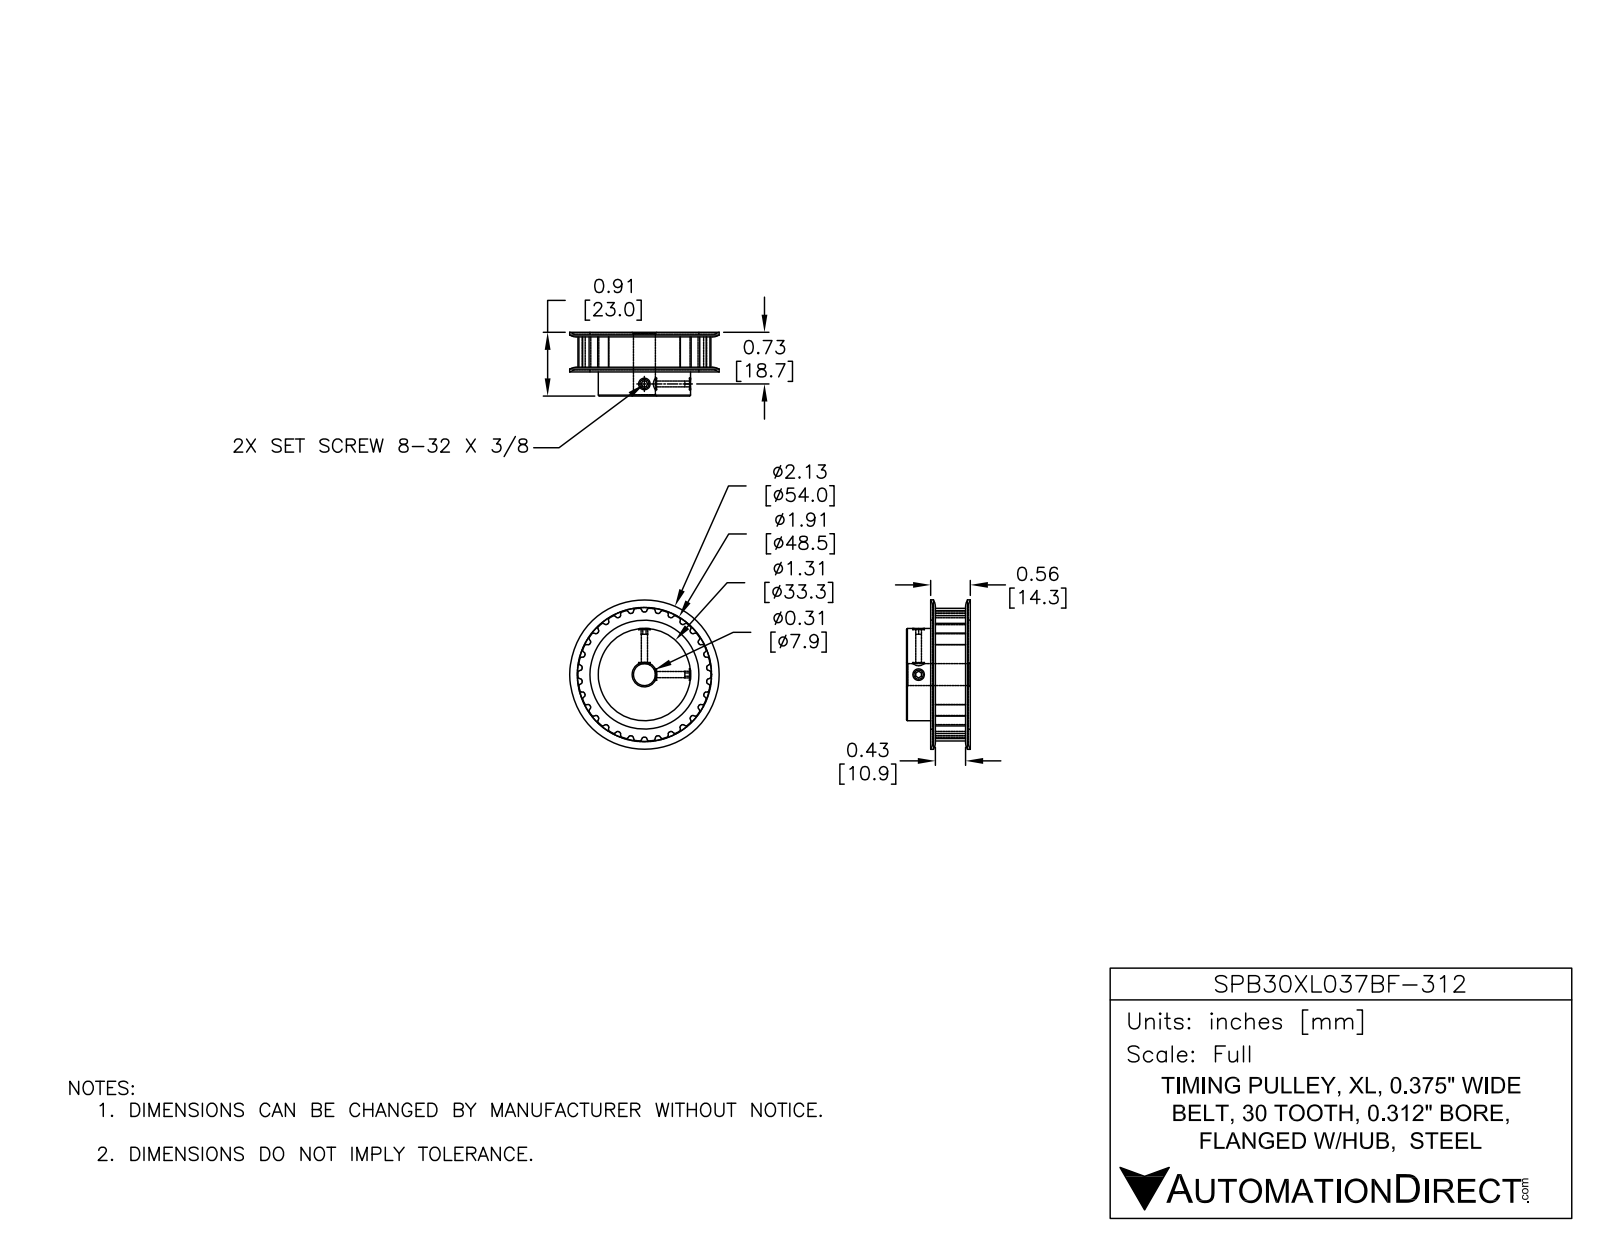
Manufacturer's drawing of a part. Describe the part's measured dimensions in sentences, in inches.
The part is named "SPB30XL037BF-312". Its 3-D file was written by "SolidWorks 2017 (AUTOMOTIVE_DESIGN)". It is 3 solids with 323 faces: 114 planar, 189 cylindrical and 20 other. Overall it measures 2.126 by 2.126 by 0.907 inches. Its volume is 1.897 cubic inches and its surface area 15.62 square inches. Round holes: 2 of diameter 0.136, 1 of diameter 0.313. Round bosses or shafts: 1 of diameter 2.126, 1 of diameter 1.551, 1 of diameter 1.311. Partial cylindrical surfaces (rounded edges, fillets, slot ends): 120 of radius 0.024, 1 of radius 0.945. The main face-to-face distances are 0.535, 0.907, 0.372, 0.028, 0.508, 0.88, 0.039, 0.469, 0.067, 0.841.
